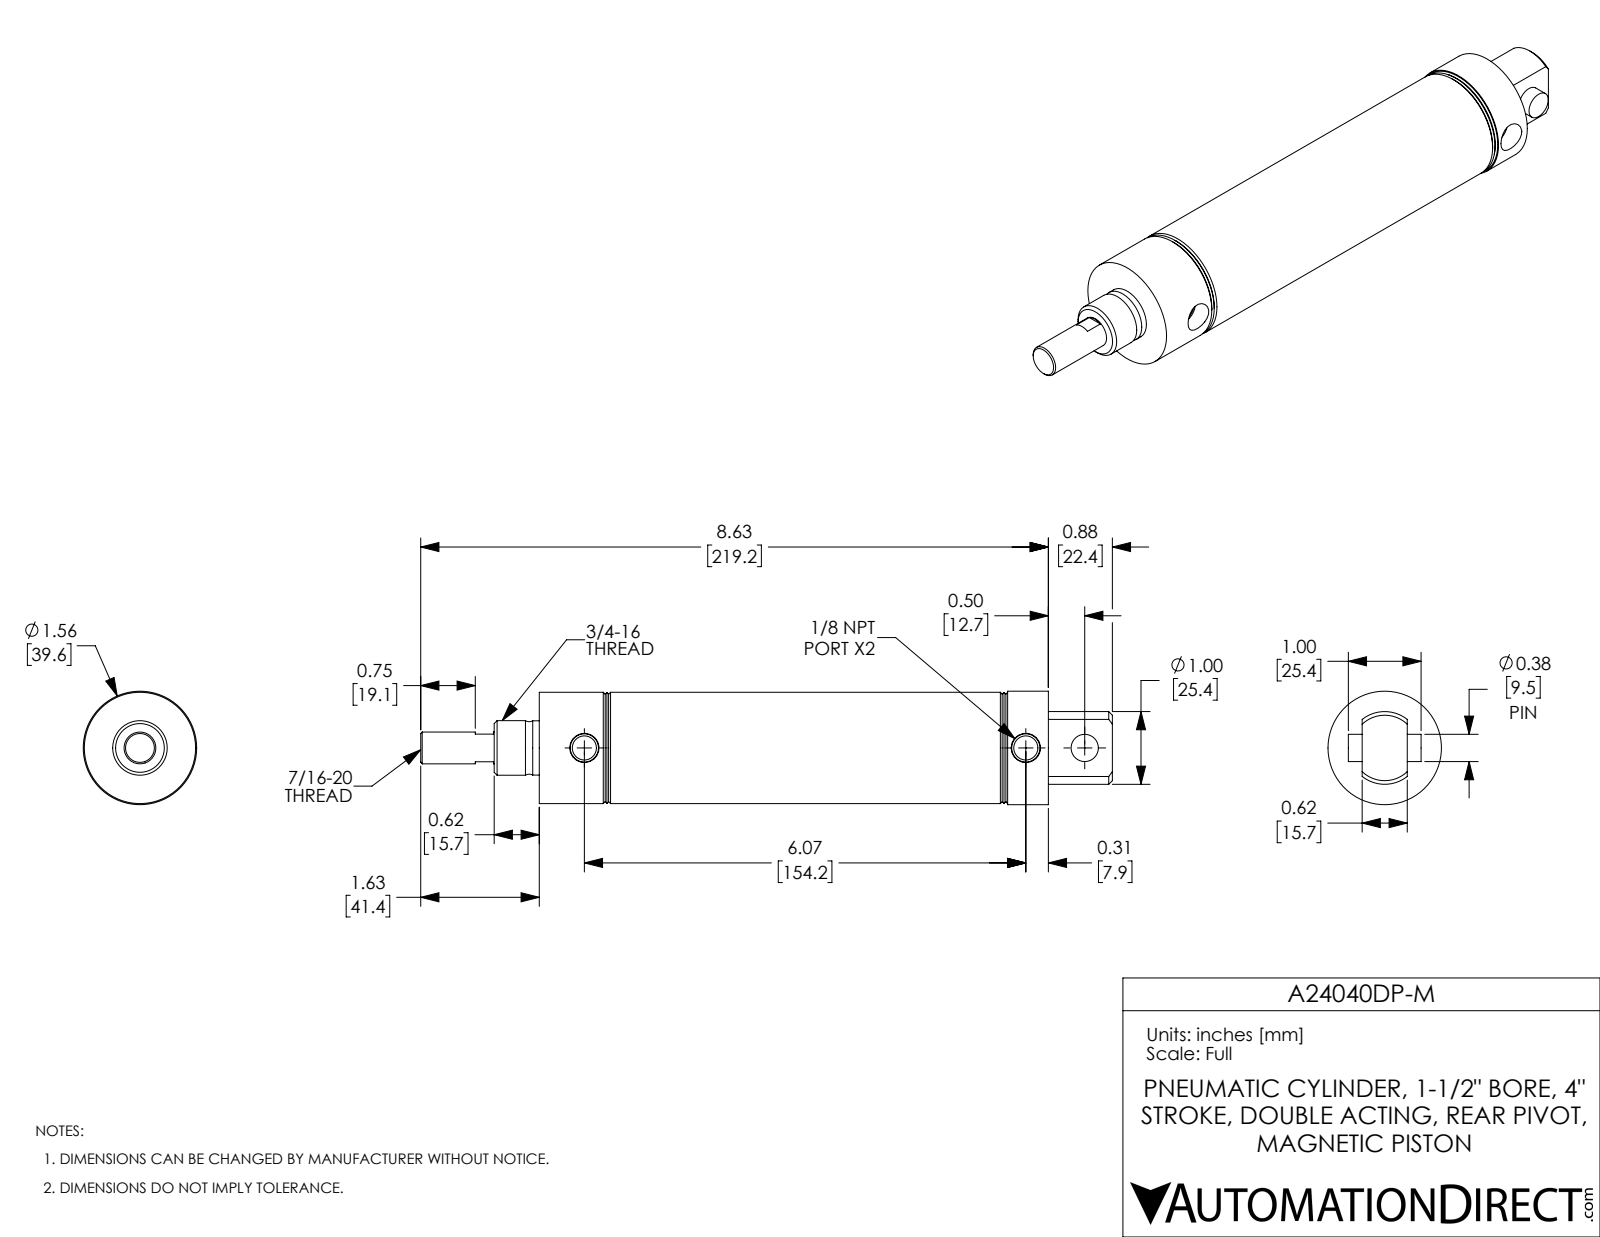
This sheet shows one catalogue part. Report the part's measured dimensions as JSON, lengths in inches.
{"part_name": "A24040DP-M; A24040DP-M-Rod; A24040DP-M-MainBody; A24040DP-M-Pin", "step_written_by": "SolidWorks 2017 (AUTOMOTIVE_DESIGN)", "units": "inches", "bodies": {"solids": 3, "faces": 84, "planar": 22, "cylindrical": 28, "other": 34}, "overall_size": [9.51, 1.56, 1.56], "volume_in3": 7.295, "surface_area_in2": 87.06, "round_holes": [[0.332, 2], [0.375, 1], [0.437, 1], [1.5, 1]], "round_bosses_or_shafts": [[1.56, 1], [1.53, 1], [0.75, 1], [0.746, 1]], "partial_cylinders_radius": [[0.5, 1]], "face_to_face_distances": [1.25, 5.75, 4.5, 0.5, 4, 5.25, 1.75, 7, 0.62, 0.88], "hole_center_spacings": [0.81, 6.07, 6.88]}
